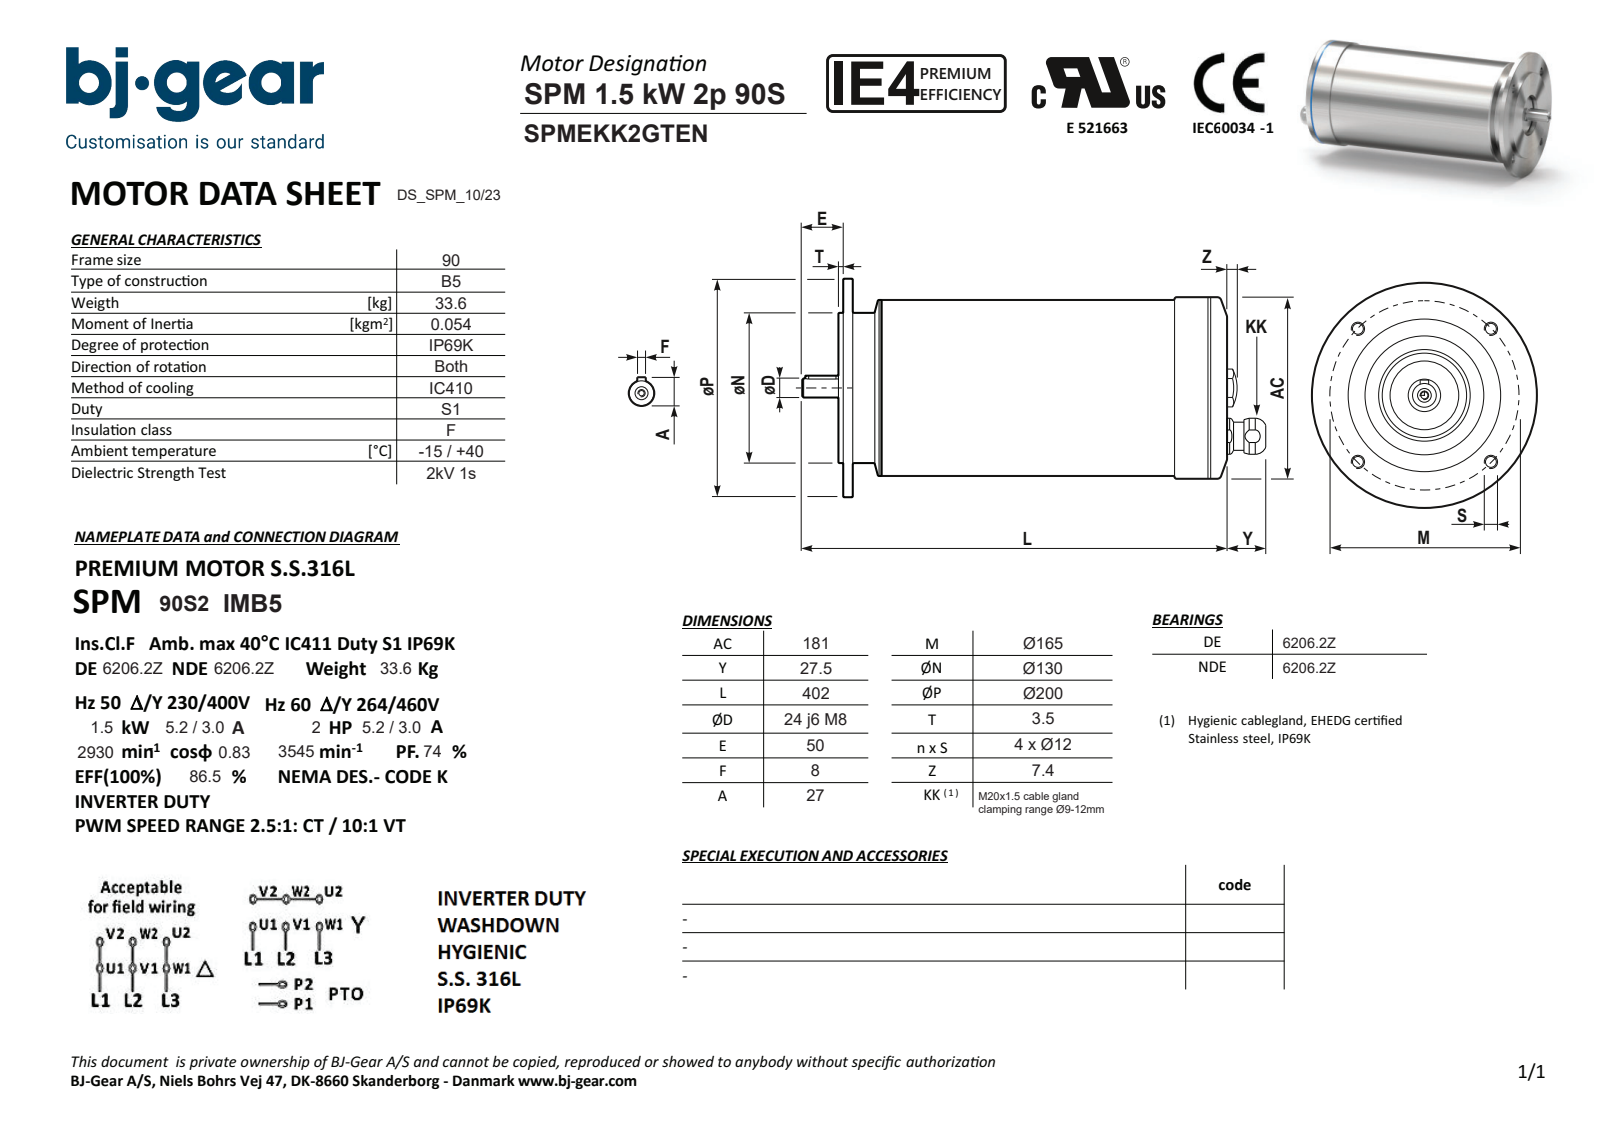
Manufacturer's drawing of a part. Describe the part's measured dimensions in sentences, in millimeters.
The part is named "SPMEKK2GTENN4KSA1-N---NNN". Its 3-D file was written by "Solid Edge (AUTOMOTIVE_DESIGN)". It is 1 solid with 86 faces: 31 planar, 30 cylindrical and 25 other. Overall it measures 429.5 by 200 by 200 millimeters. Its volume is 8 632 000 cubic millimeters and its surface area 282 681 square millimeters. Round holes: 4 of diameter 12, 1 of diameter 4.92, 1 of diameter 7, 1 of diameter 8.4, 1 of diameter 13.4, 1 of diameter 85. Round bosses or shafts: 1 of diameter 200, 1 of diameter 181, 1 of diameter 180.98, 1 of diameter 178, 1 of diameter 177.98, 1 of diameter 142, 1 of diameter 130, 1 of diameter 30. Partial cylindrical surfaces (rounded edges, fillets, slot ends): 2 of radius 4, 1 of radius 12.8. The main face-to-face distances are 352, 8, 344, 355.5, 11.5, 3.5, 6, 2, 346, 9.5. The hole center spacings are 82.51, 116.68, 58.44, 127.47, 165.01, 55.
